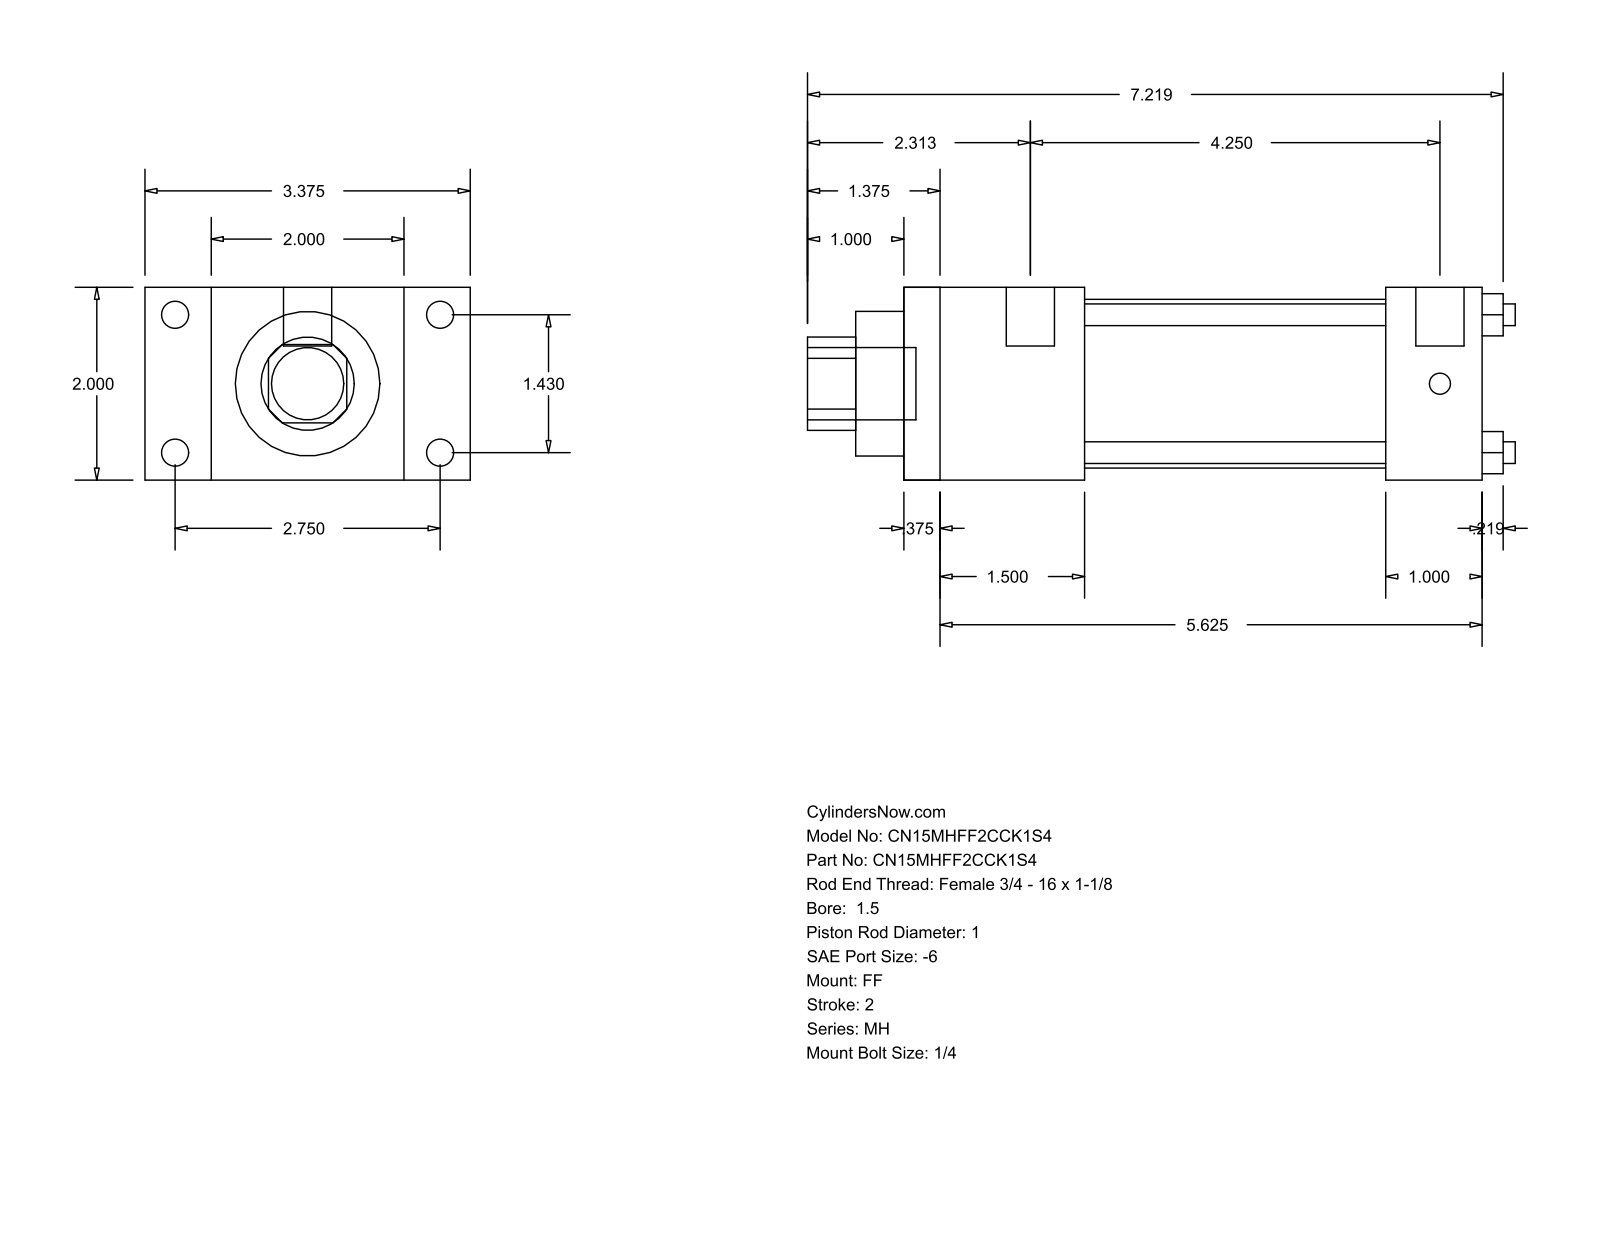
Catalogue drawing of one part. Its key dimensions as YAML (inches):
part_name: "MH_FF__0150_1"
step_written_by: "GSSL Pune (CONFIG_CONTROL_DESIGN)"
units: inches
bodies: {solids: 0, faces: 92, planar: 64, cylindrical: 28, other: 0}
overall_size: [7.344, 3.375, 2]
round_holes:
  - {diameter: 0.225, count: 4}
  - {diameter: 1, count: 1}
  - {diameter: 1.5, count: 1}
  - {diameter: 1.75, count: 1}
round_bosses_or_shafts:
  - {diameter: 0.281, count: 4}
  - {diameter: 0.219, count: 4}
  - {diameter: 0.5, count: 2}
  - {diameter: 0.75, count: 1}
partial_cylinders:
  - {radius: 0.484, count: 1}
face_to_face_distances: [2, 6, 0.375, 5.625, 1, 0.687, 2.687, 1.875, 1.5, 4.125]
hole_center_spacings: [1.011, 1.43, 2.022]
